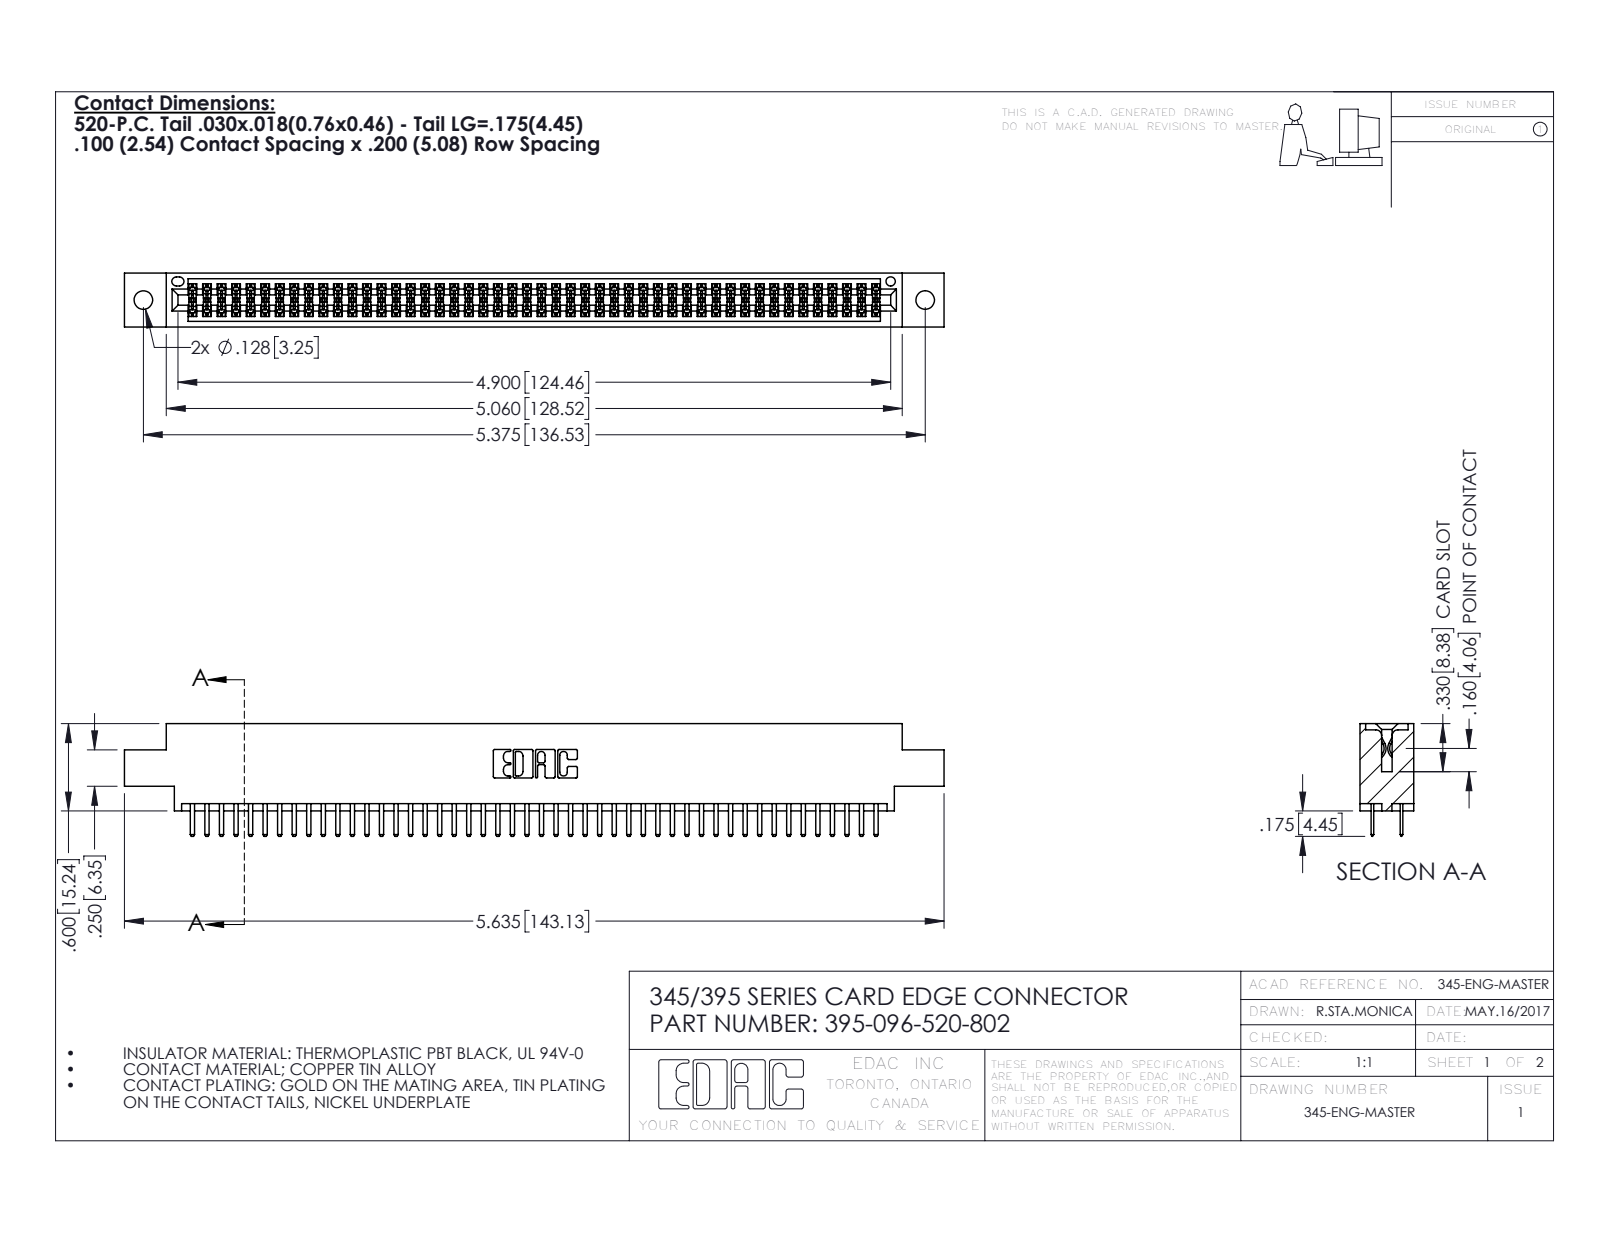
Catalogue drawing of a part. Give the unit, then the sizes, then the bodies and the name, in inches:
Units: inches
Overall size (bounding box): 5.635 × 0.775 × 0.37
Round holes (diameter × count): ⌀0.128 ×2, ⌀0.064 ×1
Partial cylindrical surfaces — rounded edges, fillets, slot ends (radius × count): R0.006 ×144, R0.01 ×100, R0.01 ×22, R0.007 ×6, R0.031 ×6, R0.026 ×3, R0.014 ×2, R0.019 ×2
Main face-to-face distances: 0.072, 0.298, 0.2, 0.37, 0.098, 0.272, 0.025, 0.225, 0.022, 0.072
Hole centre spacings: 0.27, 5.139, 5.375
Volume: 0.84 in³ · Surface area: 31.38 in²
Bodies: 97 solids, 5314 faces (3444 planar, 1870 cylindrical, 0 other)
Part name (STEP PRODUCT): 345-292-001_345-293-120; 395-096-520-802; 345 Part_0.170 Offset - 0.128 Dia
STEP written by: SolidWorks 2016 (CONFIG_CONTROL_DESIGN)
